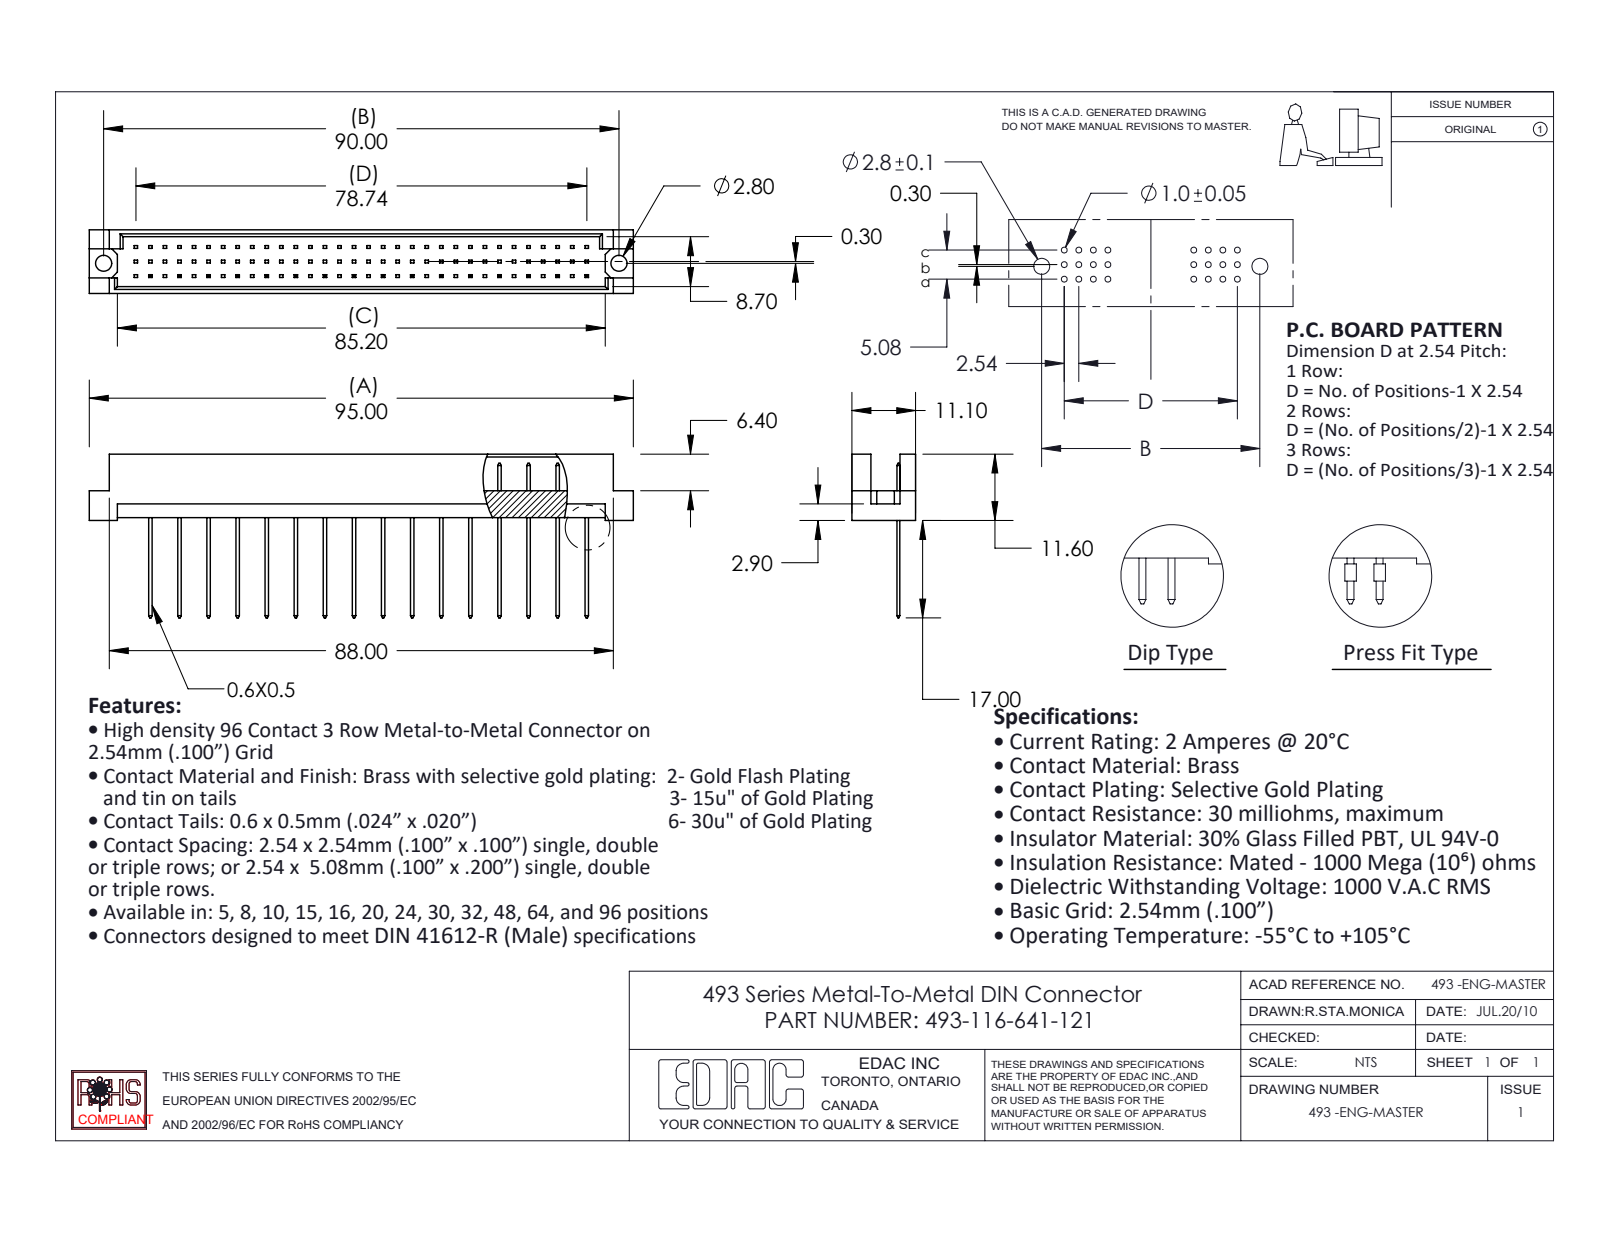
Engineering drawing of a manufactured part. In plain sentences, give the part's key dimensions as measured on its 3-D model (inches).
The part is named "493-290_41; 493 Part_96; 493-116-641-121". Its 3-D file was written by "SolidWorks 2020 (CONFIG_CONTROL_DESIGN)". It is 17 solids with 660 faces: 656 planar, 4 cylindrical and 0 other. Overall it measures 3.74 by 1.126 by 0.437 inches. Its volume is 0.353 cubic inches and its surface area 11.5 square inches. Round holes: 2 of diameter 0.11. The main face-to-face distances are 0.047, 0.39, 0.437, 0.343, 0.185, 0.02, 0.2, 0.128, 0.309, 0.081. The hole center spacings are 3.543.
